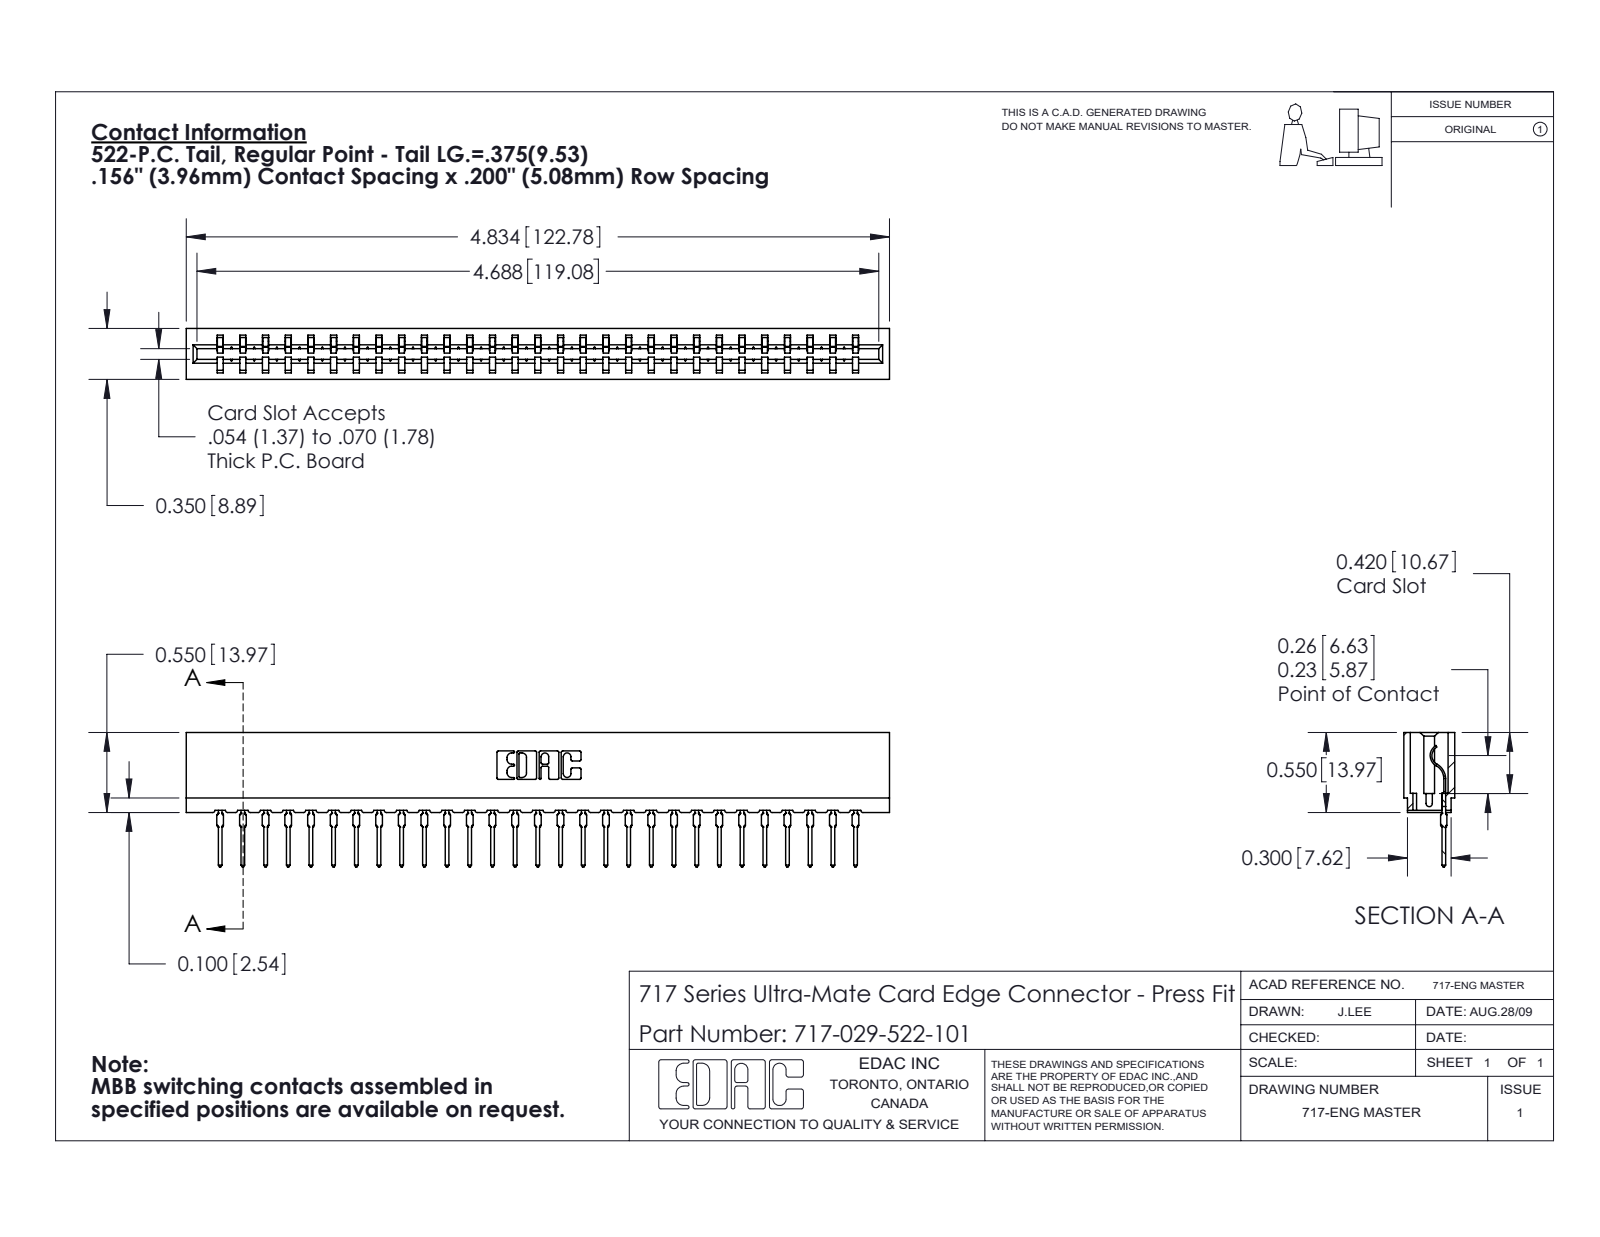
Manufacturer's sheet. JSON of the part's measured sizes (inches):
{"part_name": "717-029-522-101; 745-292-001_522; 717 Part_Insulator Option - 06", "step_written_by": "SolidWorks 2020 (CONFIG_CONTROL_DESIGN)", "units": "inches", "bodies": {"solids": 30, "faces": 3371, "planar": 2026, "cylindrical": 591, "other": 754}, "overall_size": [4.834, 0.924, 0.35], "volume_in3": 0.637, "surface_area_in2": 22.61, "partial_cylinders_radius": [[0.015, 58], [0.021, 58], [0.01, 22], [0.007, 6], [0.031, 6], [0.005, 4], [0.011, 4], [0.026, 3]], "face_to_face_distances": [0.212, 0.138, 0.35, 0.074, 0.156, 0.045, 0.305, 0.093, 0.167, 0.063]}
